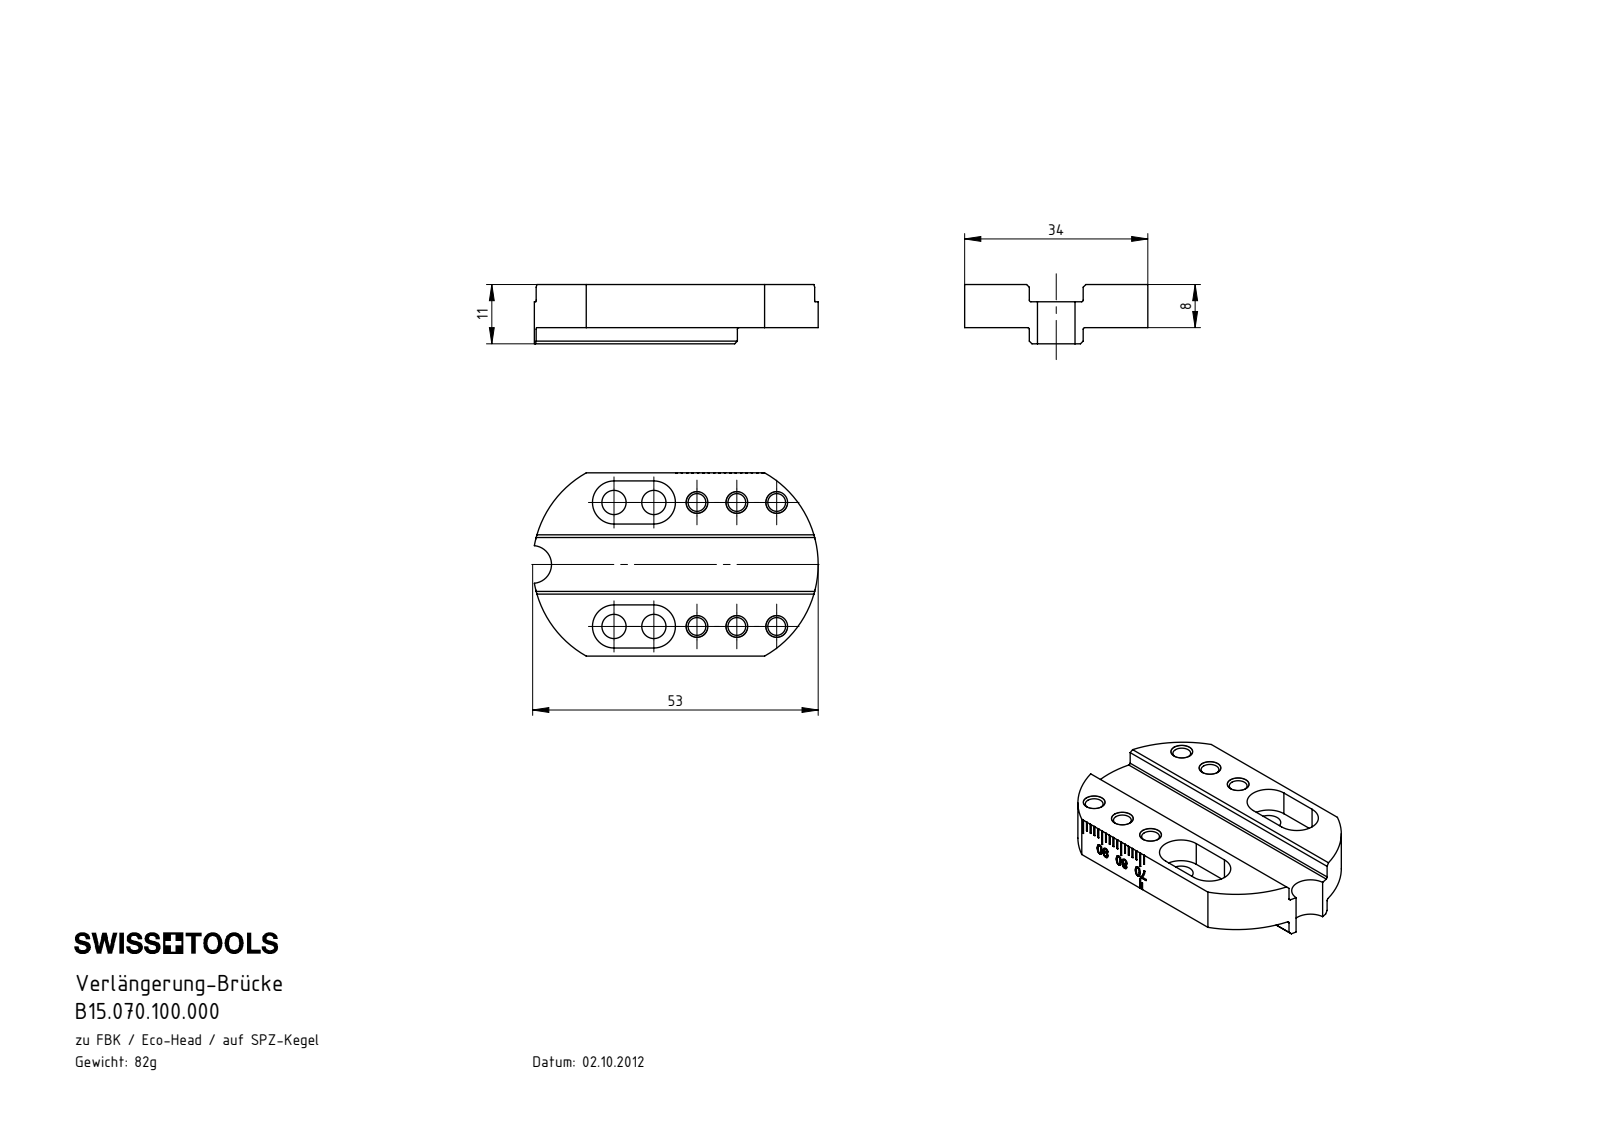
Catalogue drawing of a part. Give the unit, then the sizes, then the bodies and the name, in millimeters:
Units: millimetres
Overall size (bounding box): 52.69 × 34 × 11
Round holes (diameter × count): ⌀3.3 ×6, ⌀4.5 ×4
Partial cylindrical surfaces — rounded edges, fillets, slot ends (radius × count): R0.3 ×5, R4 ×4, R19.5 ×2, R3.5 ×1
Main face-to-face distances: 8, 4.8, 3.2, 12, 22, 3, 7.8, 11, 34, 1.5
Hole centre spacings: 7.4, 24.16, 23, 15.4, 22.8, 27.68, 32.39, 8
Volume: 10 481 mm³ · Surface area: 5 681 mm²
Bodies: 1 solid, 208 faces (117 planar, 23 cylindrical, 68 other)
Part name (STEP PRODUCT): EH1.EB1.053.008
STEP written by: SolidWorks 2017 (AUTOMOTIVE_DESIGN)
